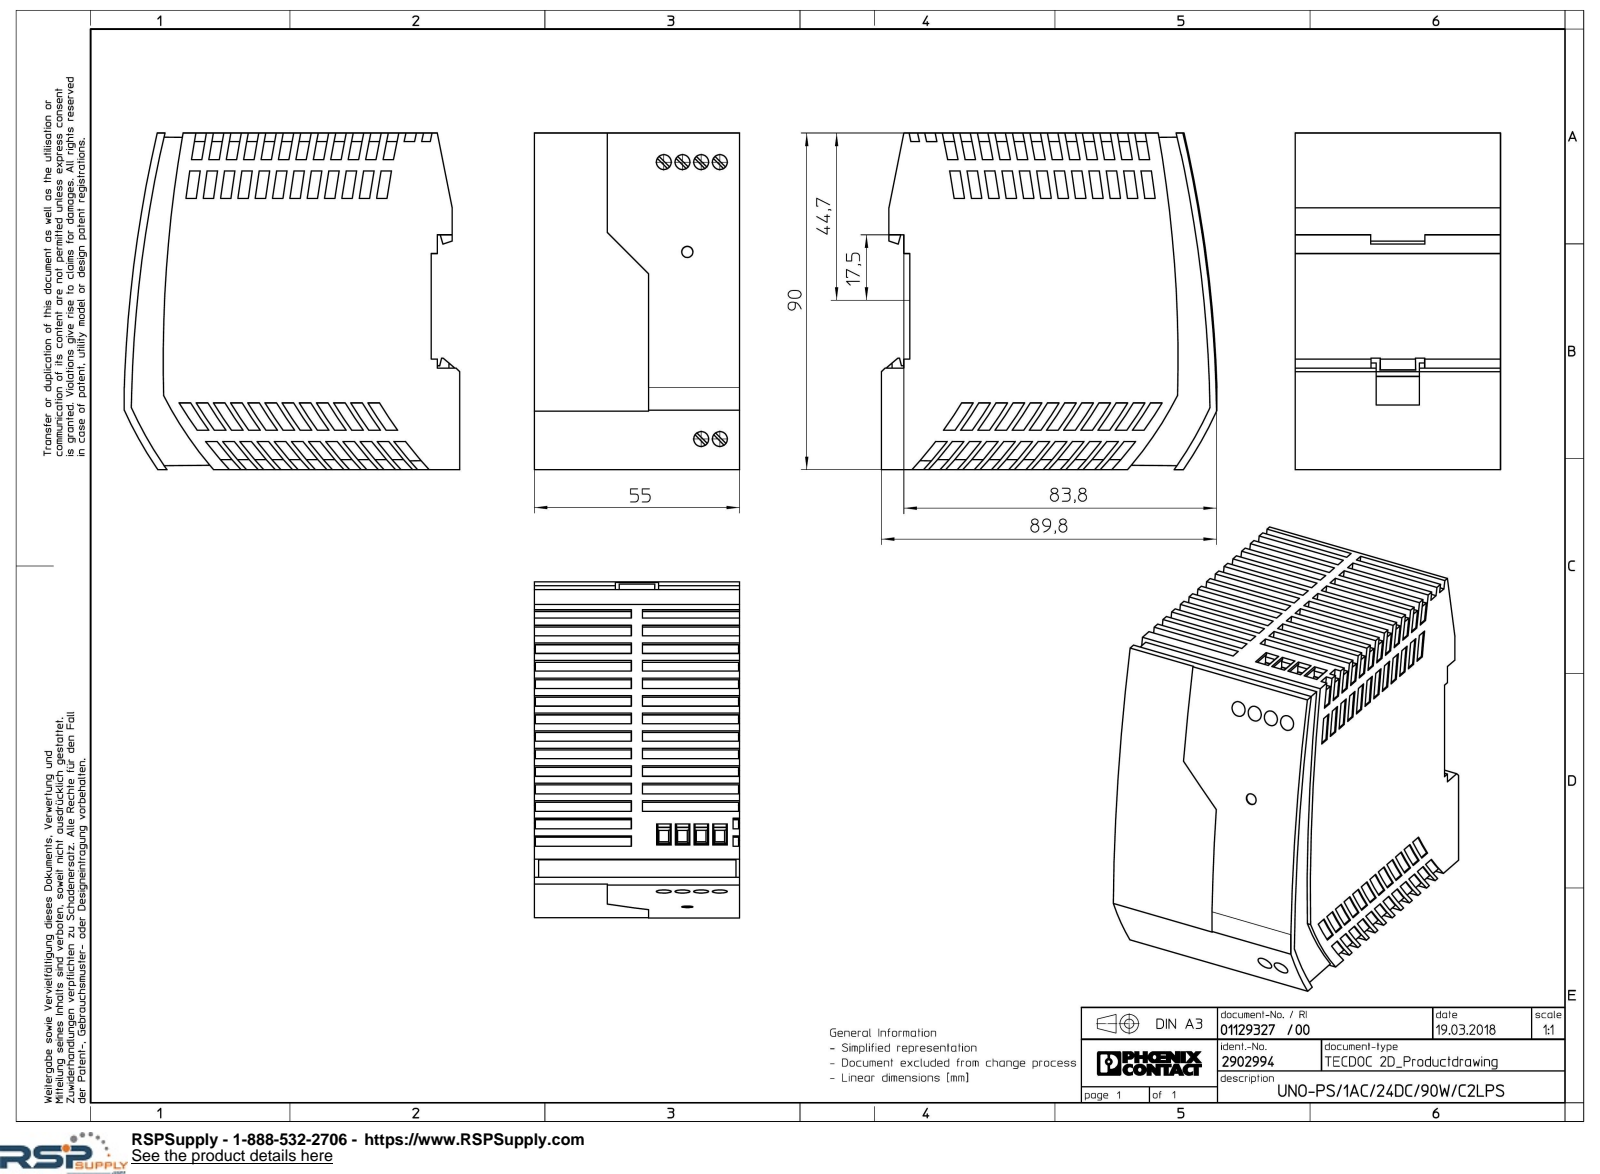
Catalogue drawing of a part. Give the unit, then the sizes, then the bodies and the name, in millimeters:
Units: millimetres
Overall size (bounding box): 90 × 89.87 × 55
Round holes (diameter × count): ⌀4 ×6
Partial cylindrical surfaces — rounded edges, fillets, slot ends (radius × count): R111 ×26, R98 ×1, R98.55 ×1, R100 ×1, R282.66 ×1, R284.9 ×1, R286.76 ×1, R291.36 ×1
Main face-to-face distances: 55, 2.3, 87.7, 90, 2.7, 85, 87.3, 54.7, 7.6, 54.4
Hole centre spacings: 5, 74.17, 10, 74, 74.67, 15, 75.5
Volume: 395 571 mm³ · Surface area: 43 992 mm²
Bodies: 1 solid, 779 faces (558 planar, 219 cylindrical, 2 other)
Part name (STEP PRODUCT): UNO_PS_1AC_24DC_90W_C2LPS-select
STEP written by: Creo Elements/Direct Modeling 20.1A 29-Sep-2018 (C) Parametric Technology GmbH (AUTOMOTIVE_DESIGN)
